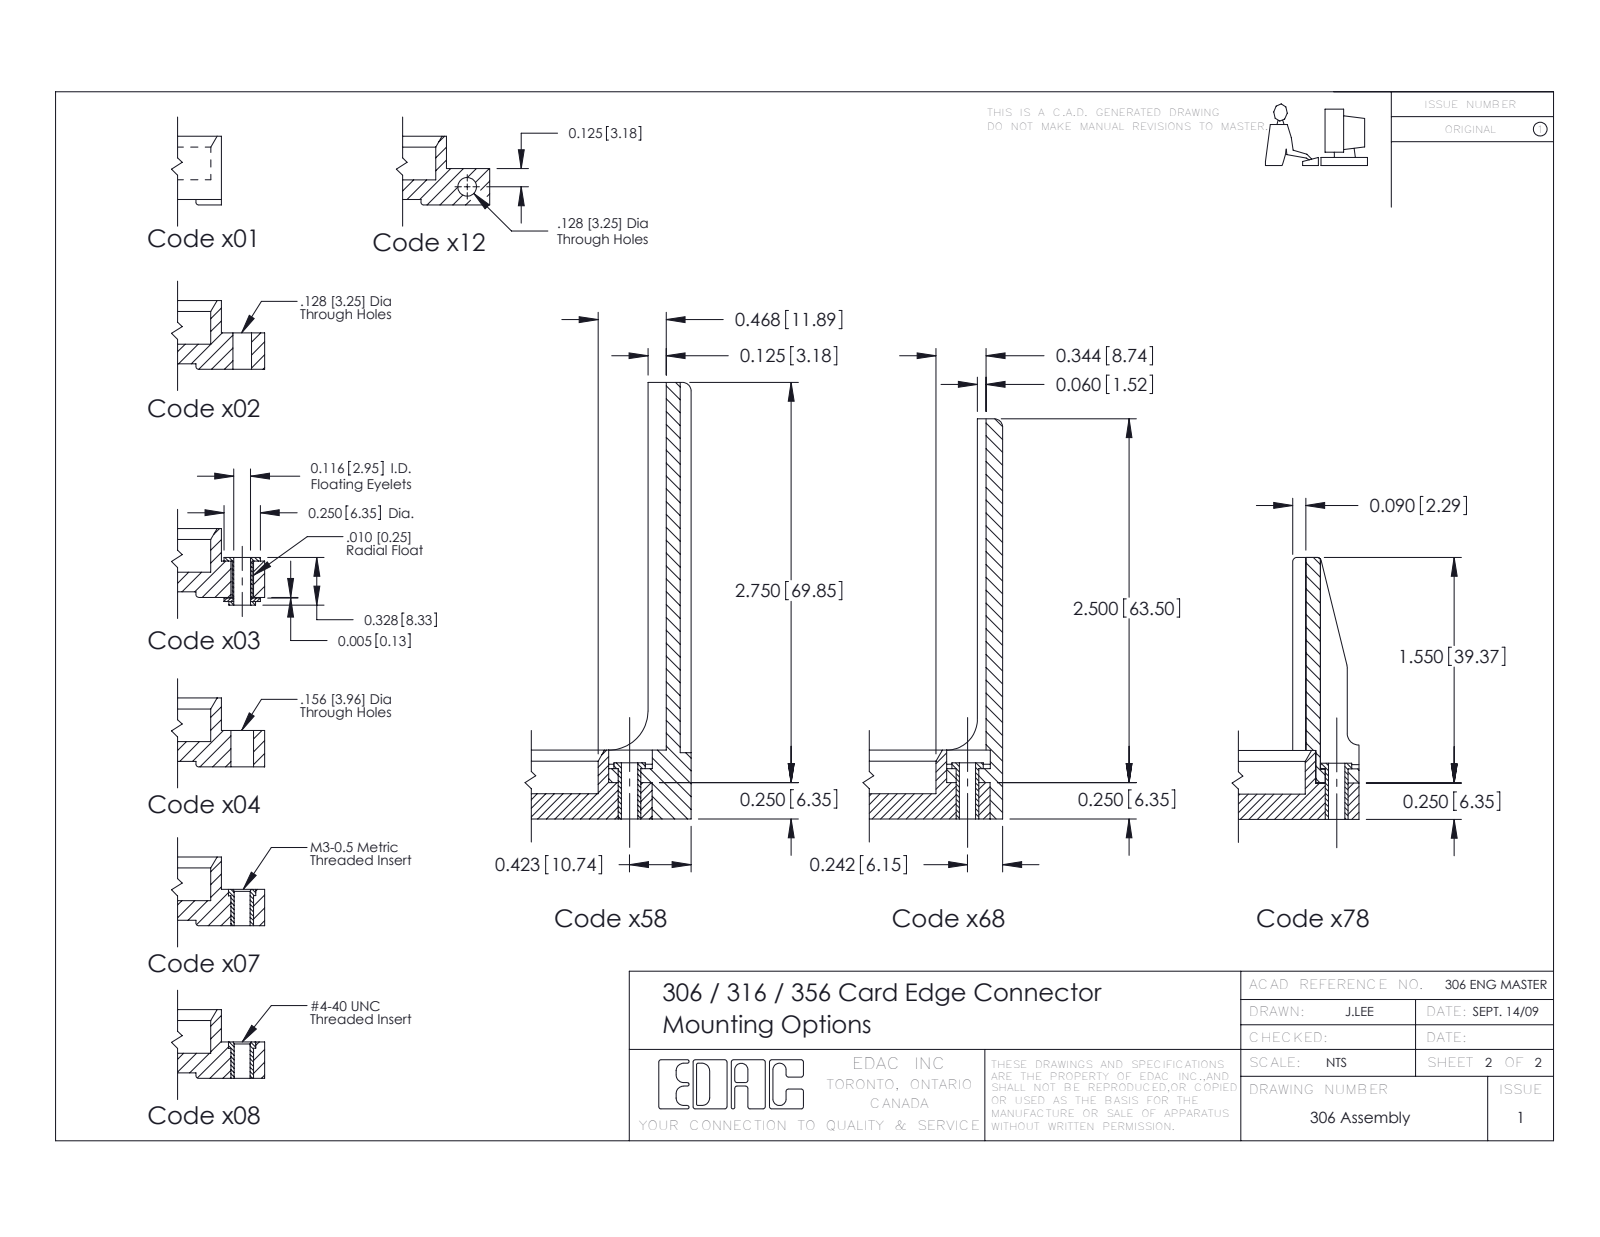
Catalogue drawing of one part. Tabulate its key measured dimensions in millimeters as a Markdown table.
| quantity | value |
| --- | --- |
| part name | 306 Part_.128 Dia; 306-040-520-102; 306-290-001_120 |
| STEP written by | SolidWorks 2016 (CONFIG_CONTROL_DESIGN) |
| units | millimeters |
| bodies | 41 solids, 2916 faces (1948 planar, 808 cylindrical, 160 other) |
| overall size | 181.5 × 17.1 × 12.7 |
| volume | 20 020 mm³ |
| surface area | 20 270 mm² |
| round holes (diameter × count) | 3.3 × 2 |
| partial cylindrical surfaces (radius × count) | 0.4 × 125, 0.6 × 40, 0.3 × 22, 0.2 × 6, 0.8 × 6, 0.7 × 3, 1.7 × 2, 2.1 × 2 |
| main face-to-face distances | 4.1, 8.6, 12.7, 0.4, 10.9, 2.1, 4.6, 6.2, 6.5, 2.5 |
| hole center spacings | 173.6 |
